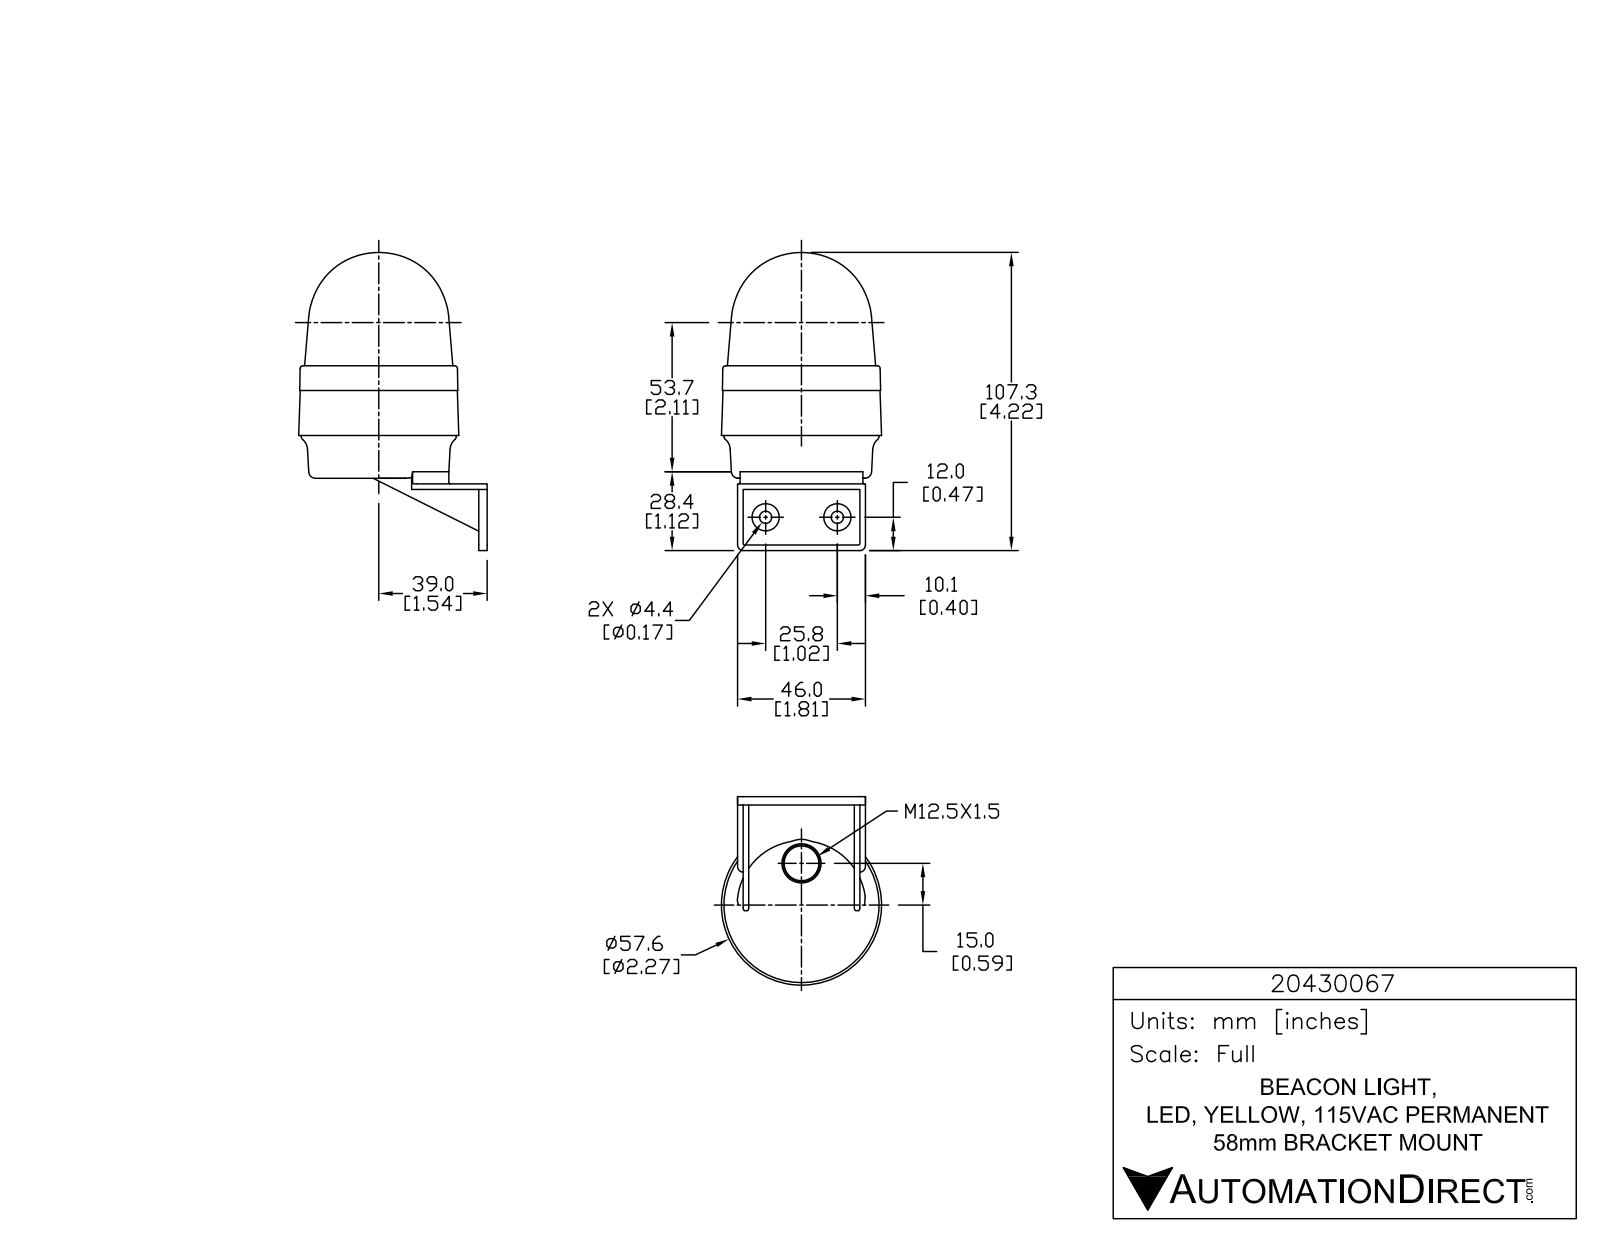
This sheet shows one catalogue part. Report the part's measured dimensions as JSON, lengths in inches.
{"part_name": "20430067", "step_written_by": "SolidWorks 2015 (AUTOMOTIVE_DESIGN)", "units": "inches", "bodies": {"solids": 1, "faces": 828, "planar": 551, "cylindrical": 179, "other": 98}, "overall_size": [4.225, 2.852, 2.407], "volume_in3": 10.27, "surface_area_in2": 33.38, "round_holes": [[0.039, 3], [0.173, 2]], "round_bosses_or_shafts": [[0.226, 3], [0.056, 3], [0.386, 2], [2.197, 1]], "partial_cylinders_radius": [[0.008, 6], [0.008, 6], [0.008, 6], [0.02, 6], [0.131, 6], [0.079, 4], [0.004, 3], [0.005, 3]], "face_to_face_distances": [0.079, 0.157, 1.575, 1.654, 0.039, 0.118, 1.496, 0.866, 0.945, 0.764], "hole_center_spacings": [1.016]}
